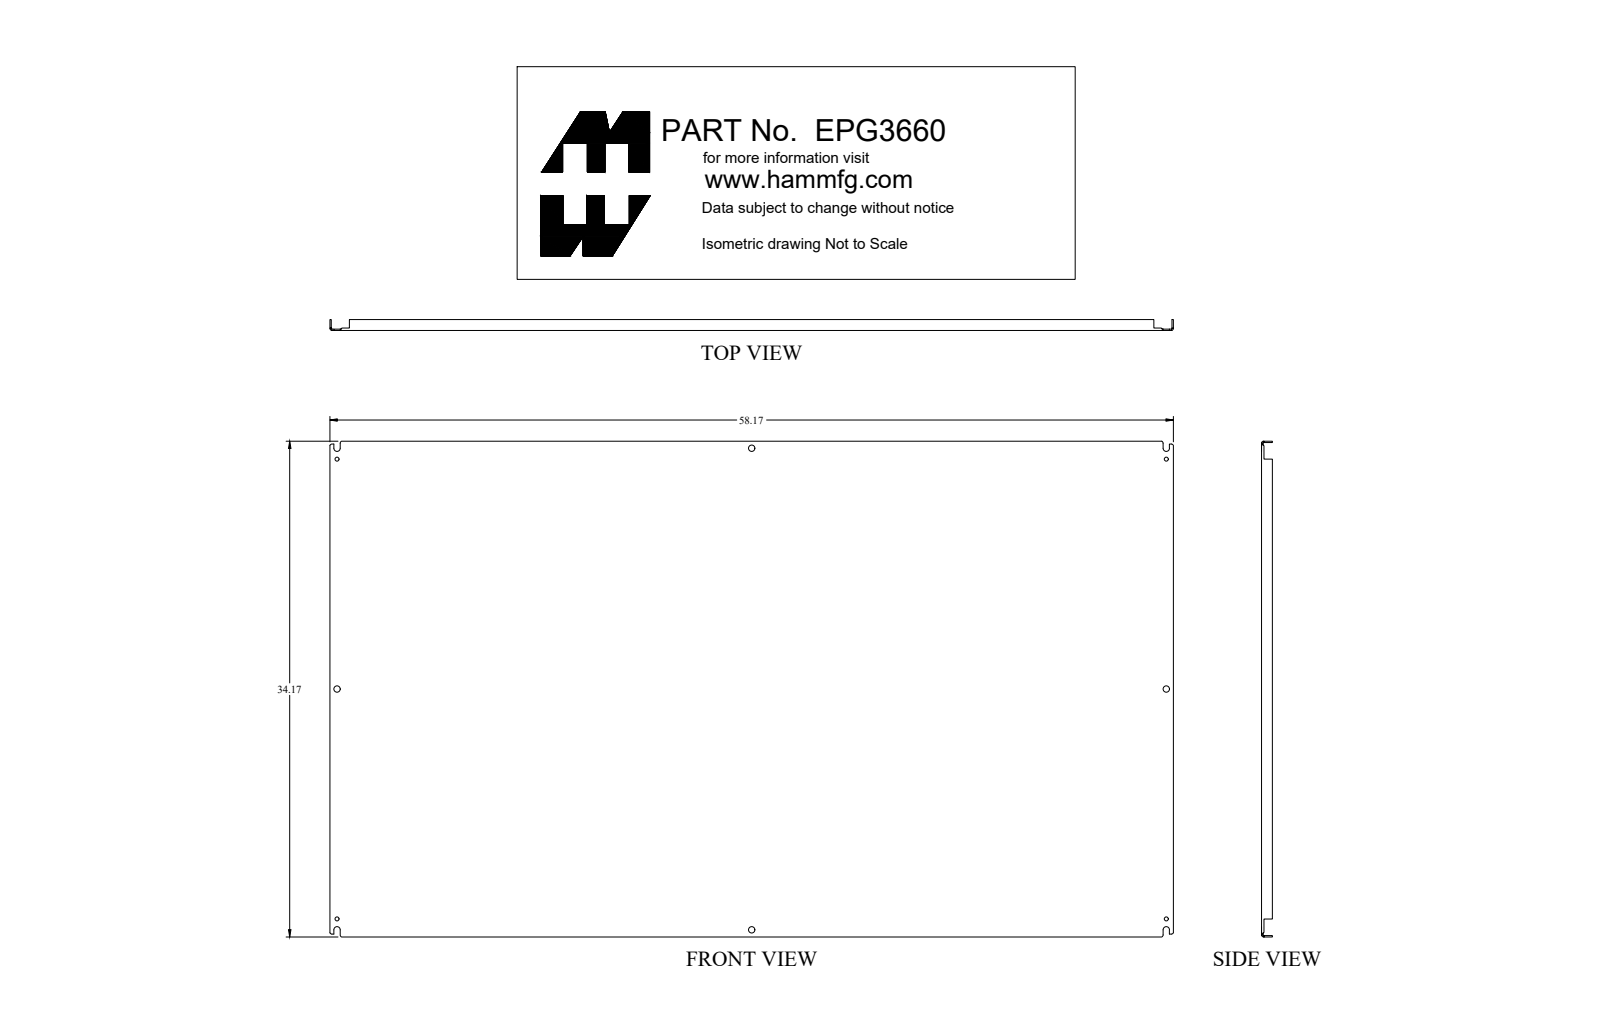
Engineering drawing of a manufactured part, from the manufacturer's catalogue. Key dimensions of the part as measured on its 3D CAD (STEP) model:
Part name (STEP PRODUCT): EPG3660
STEP written by: SolidWorks 2018 (AUTOMOTIVE_DESIGN)
Units: inches
Bodies: 1 solid, 136 faces (74 planar, 46 cylindrical, 16 other)
Overall size (bounding box): 58.17 × 34.17 × 0.75
Volume: 198.8 in³ · Surface area: 4 204 in²
Round holes (diameter × count): ⌀0.281 ×4, ⌀0.437 ×4
Partial cylindrical surfaces — rounded edges, fillets, slot ends (radius × count): R0.048 ×4, R0.063 ×4, R0.143 ×4, R0.219 ×4
Main face-to-face distances: 0.095, 34.075, 58.075, 34.17, 33.98, 58.17, 57.98, 0.75, 0.655, 0.171
Hole centre spacings: 15.844, 28.604, 33.06, 43.242, 59.343, 57.188, 31.688, 65.381
